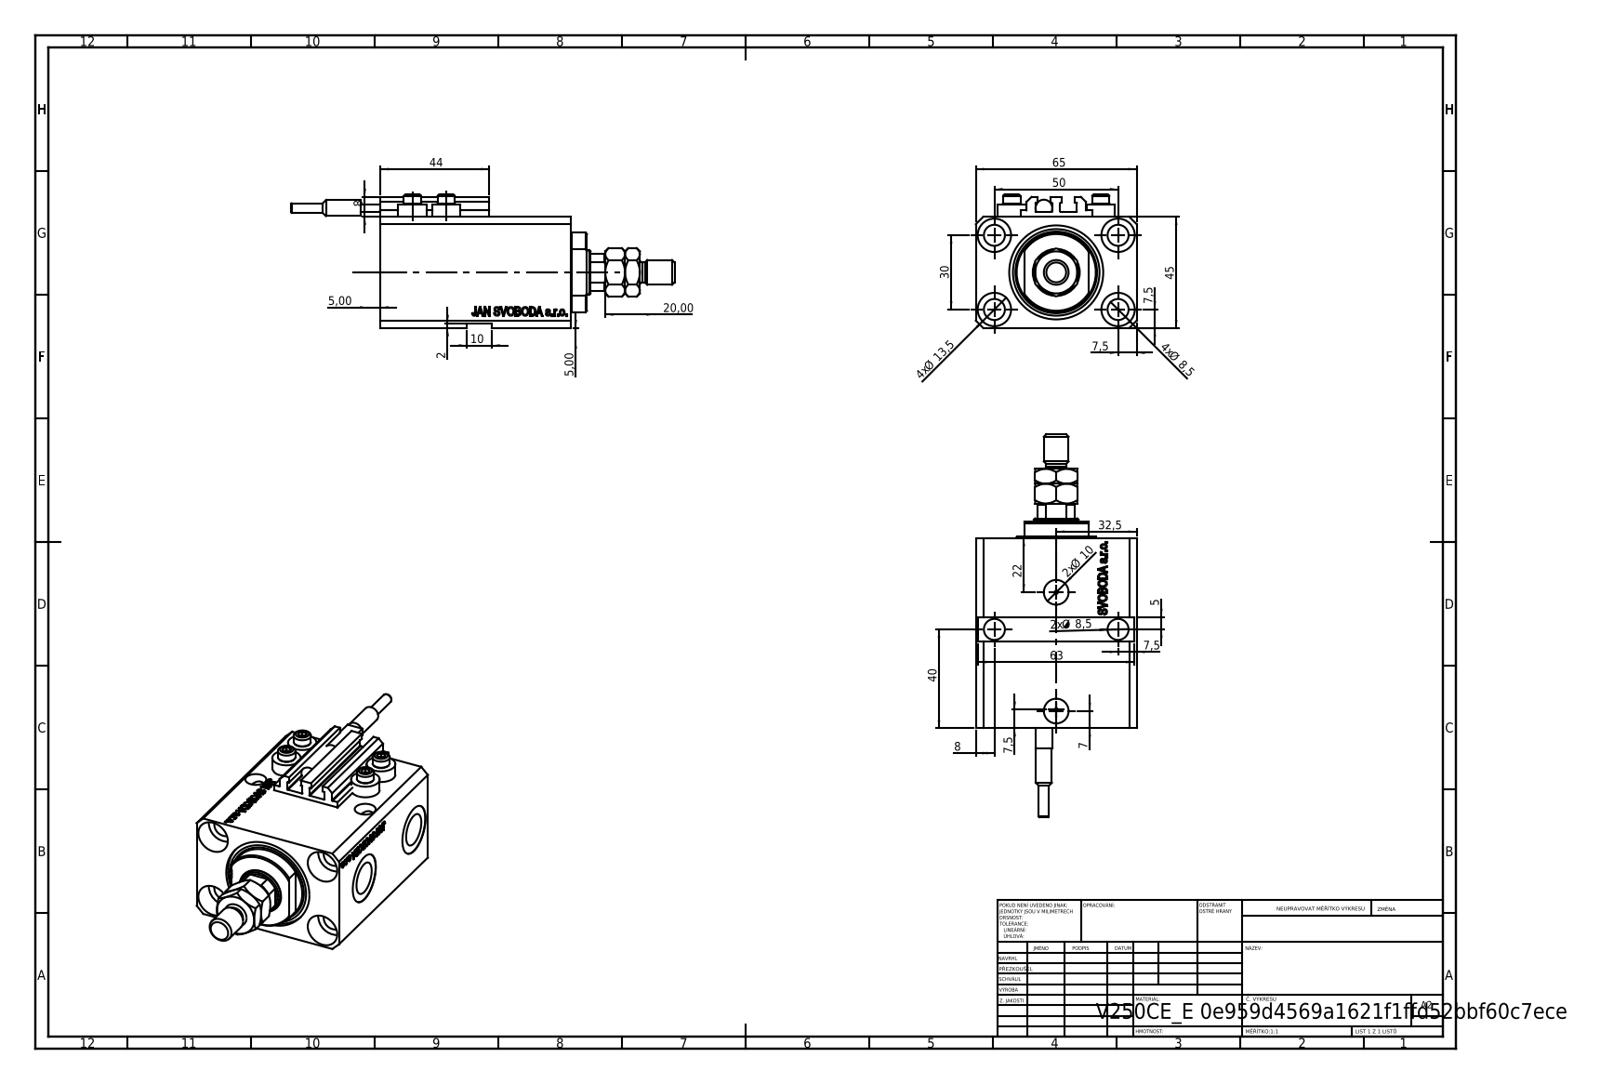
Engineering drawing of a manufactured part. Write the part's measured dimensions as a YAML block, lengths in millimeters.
part_name: "SWITCH_V250CE; V250CE_E; MTA; V250CE_C_VCP (+2 more)"
step_written_by: "SolidWorks 2019 (CONFIG_CONTROL_DESIGN)"
units: millimeters
bodies: {solids: 10, faces: 1142, planar: 542, cylindrical: 136, other: 464}
overall_size: [154.9, 65, 54]
volume: 206038
surface_area: 64404
round_holes:
  - {diameter: 8.5, count: 7}
  - {diameter: 1.25, count: 4}
  - {diameter: 4, count: 4}
  - {diameter: 13.5, count: 4}
  - {diameter: 10, count: 2}
  - {diameter: 13.16, count: 2}
  - {diameter: 20, count: 2}
  - {diameter: 18, count: 1}
  - {diameter: 25, count: 1}
  - {diameter: 38, count: 1}
round_bosses_or_shafts:
  - {diameter: 11.6, count: 4}
  - {diameter: 7, count: 4}
  - {diameter: 10, count: 1}
  - {diameter: 8, count: 1}
  - {diameter: 6.8, count: 1}
  - {diameter: 6.5, count: 1}
  - {diameter: 4, count: 1}
partial_cylinders:
  - {radius: 0.2, count: 10}
  - {radius: 8.5, count: 1}
  - {radius: 16, count: 1}
face_to_face_distances: [45, 65, 51.9, 25.1, 6.9, 77, 2, 3, 70.1, 47]
hole_center_spacings: [29.15, 50, 13.6, 15.12, 18.81, 18.97, 26.22, 26.61]
